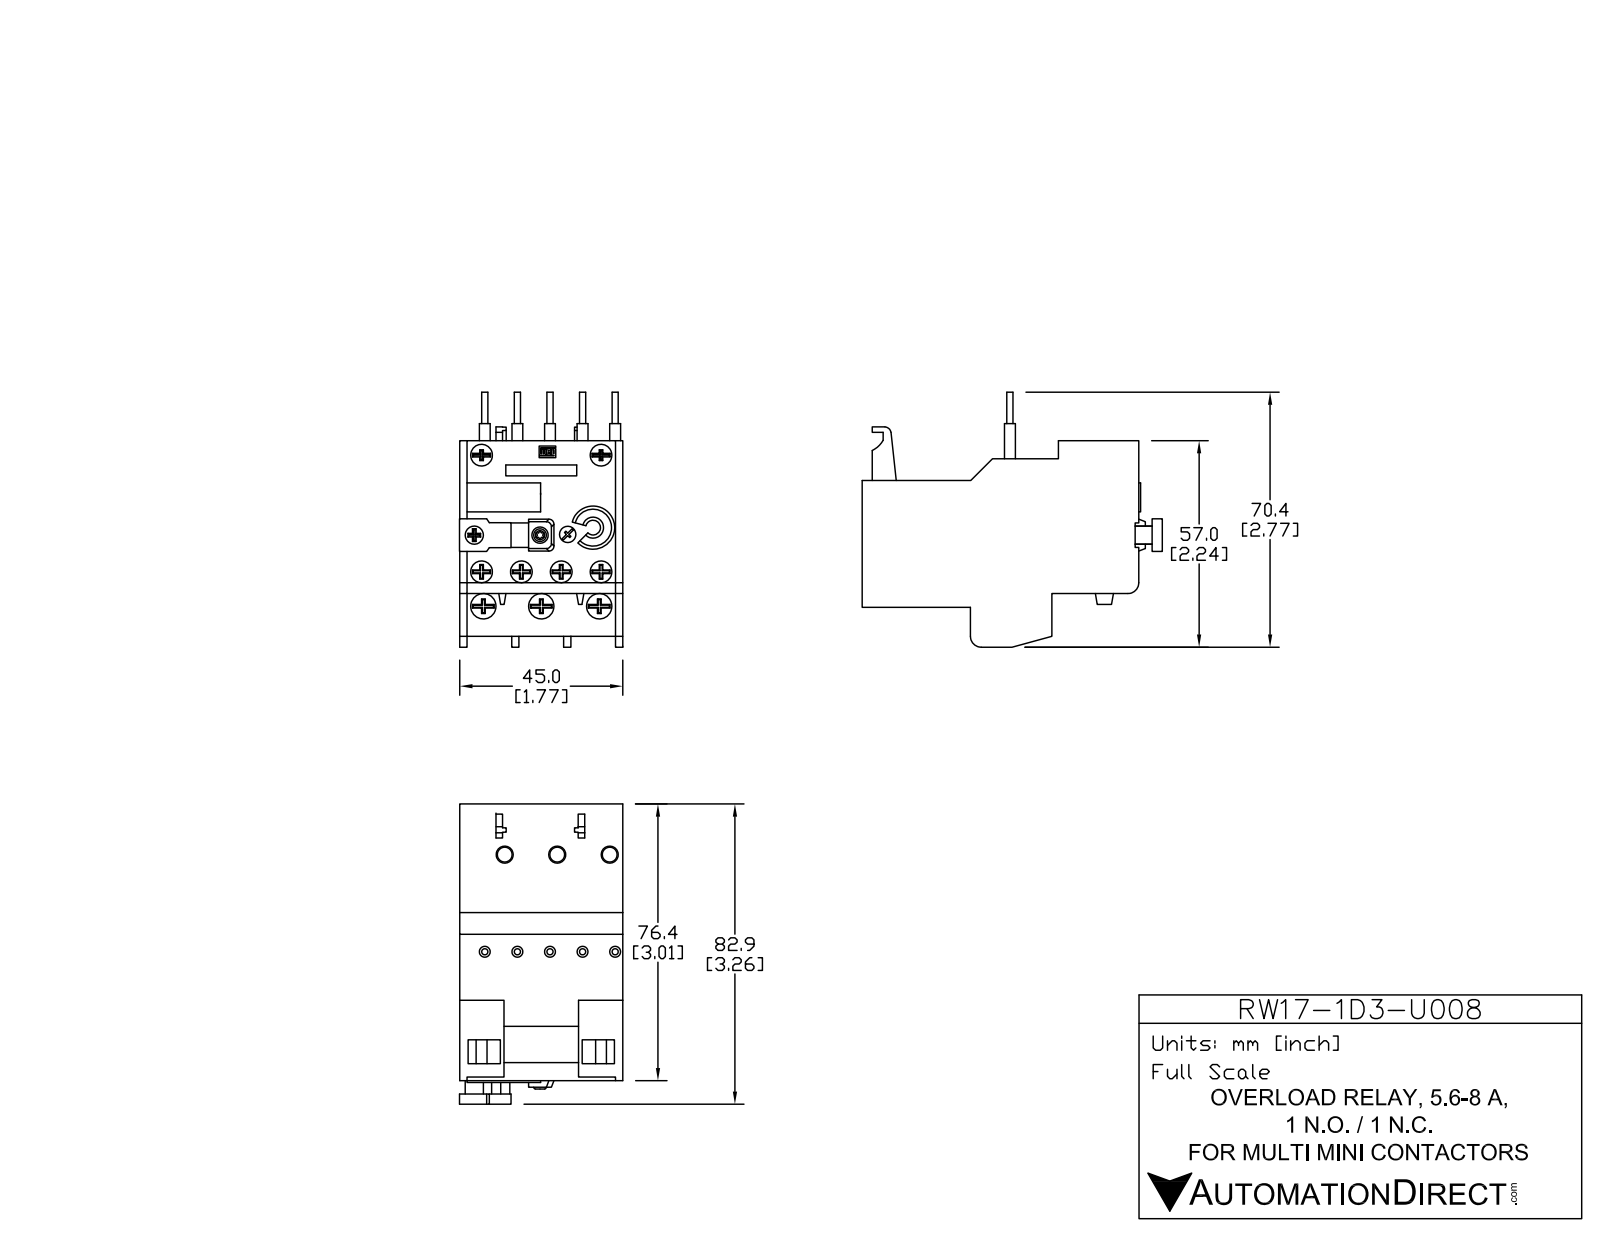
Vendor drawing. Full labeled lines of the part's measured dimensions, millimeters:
Part name (STEP PRODUCT): RW17D-1D3-U008
STEP written by: SolidWorks 2013 (AUTOMOTIVE_DESIGN)
Units: millimetres
Bodies: 18 solids, 756 faces (515 planar, 214 cylindrical, 27 other)
Overall size (bounding box): 82.65 × 70.5 × 45.55
Volume: 127 454 mm³ · Surface area: 34 704 mm²
Round holes (diameter × count): ⌀6 ×6, ⌀4 ×3, ⌀7 ×3, ⌀7.5 ×3, ⌀4.5 ×1, ⌀4.75 ×1, ⌀5.33 ×1, ⌀5.5 ×1, ⌀10.42 ×1
Round bosses / shafts (diameter × count): ⌀5.5 ×7, ⌀3 ×7, ⌀1.75 ×5, ⌀5.6 ×2, ⌀3.25 ×2, ⌀6.42 ×1, ⌀6.15 ×1, ⌀4.75 ×1
Partial cylindrical surfaces — rounded edges, fillets, slot ends (radius × count): R0.5 ×20, R0.25 ×12, R1 ×9, R4.52 ×6, R5.86 ×4, R7.86 ×4, R1.5 ×3, R1.25 ×2
Main face-to-face distances: 45.5, 1.5, 10.85, 11, 76.4, 35, 1.42, 74.98, 74.9, 6
Hole centre spacings: 15, 8.55, 10.75, 30, 10.57, 11.86, 14.25, 21.35
